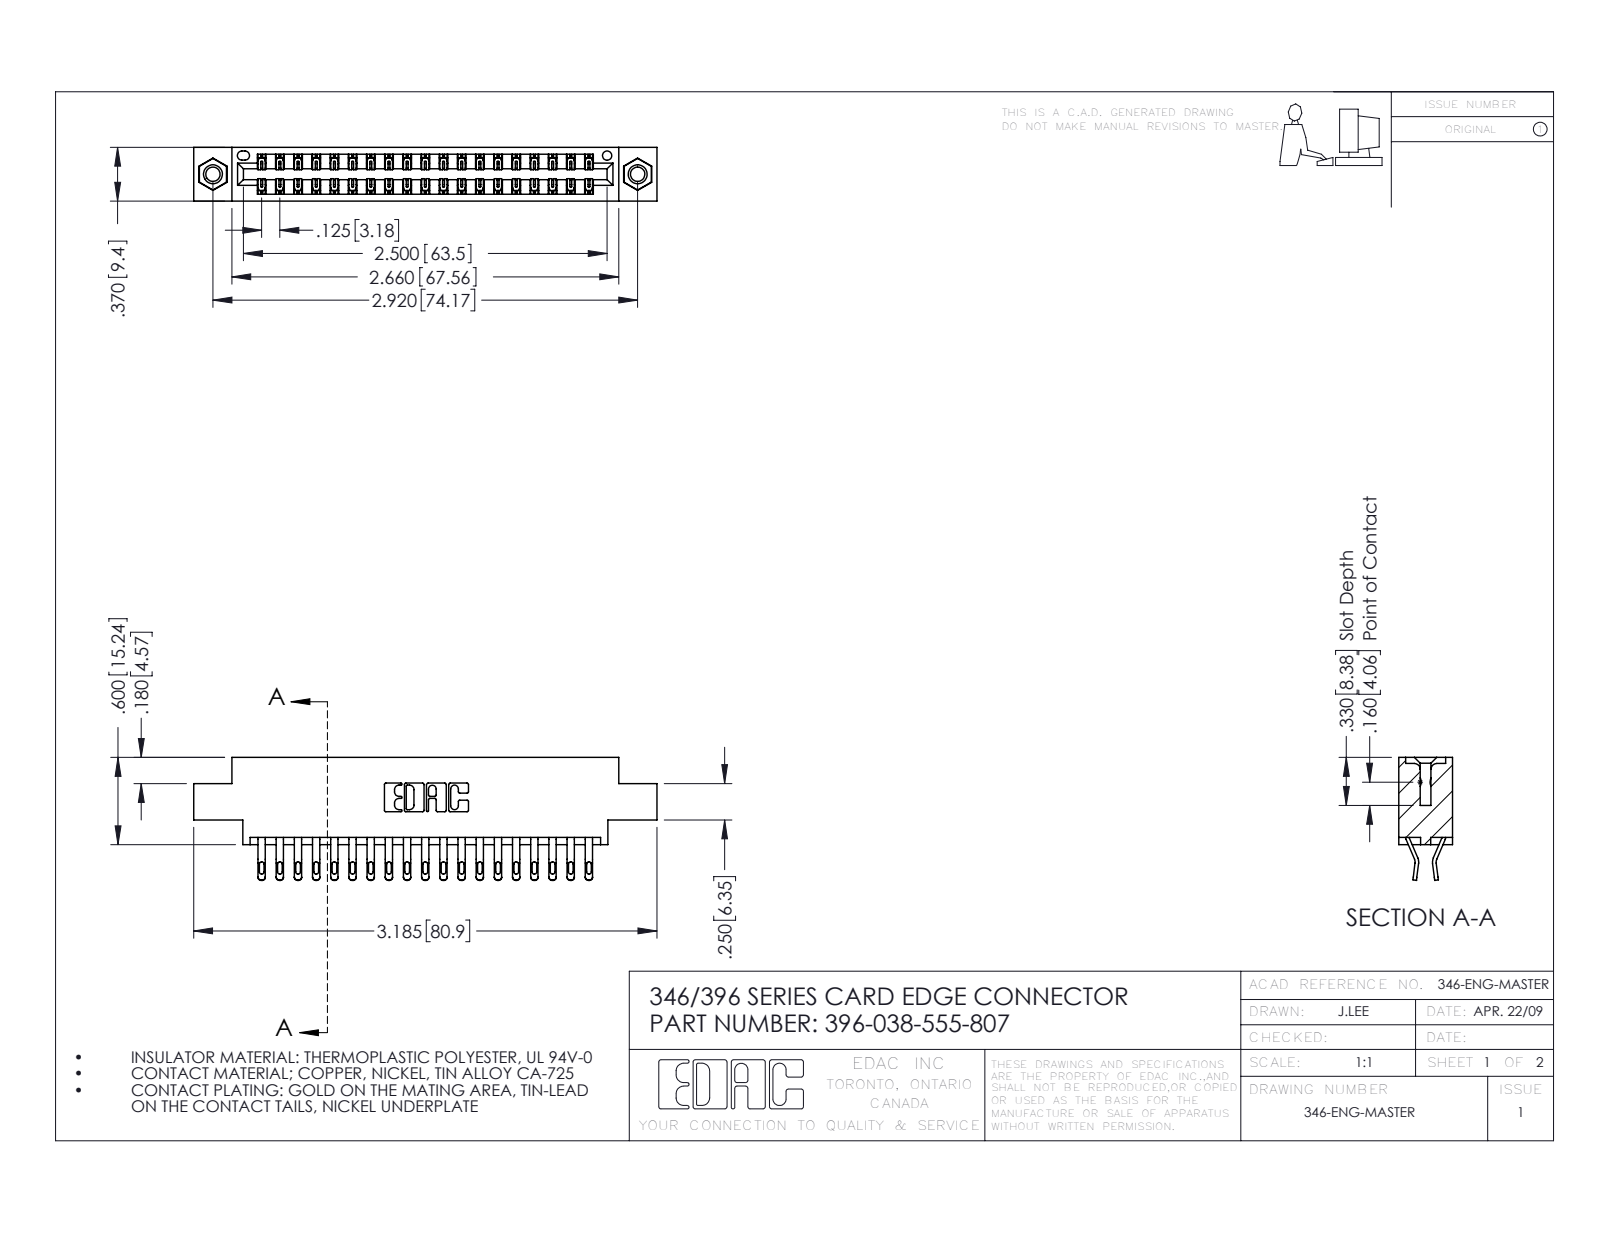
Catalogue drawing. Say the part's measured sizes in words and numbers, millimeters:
The part is named "396-038-555-807; 346 Part_0.170 Offset - 0.156 Dia-TI; 345-250-001_345-250-005-103; 345-292-001_555 Tail". Its 3-D file was written by "SolidWorks 2016 (CONFIG_CONTROL_DESIGN)". It is 41 solids with 2390 faces: 1366 planar, 1008 cylindrical and 16 other. Overall it measures 80.9 by 21.5 by 9.4 millimeters. Its volume is 7 650 cubic millimeters and its surface area 10 760 square millimeters. Round holes: 2 of diameter 2.5, 2 of diameter 3.2, 2 of diameter 4, 1 of diameter 1.6. Round bosses or shafts: 2 of diameter 3.9. Partial cylindrical surfaces (rounded edges, fillets, slot ends): 76 of radius 0.4, 76 of radius 0.5, 57 of radius 0.2, 22 of radius 0.3, 6 of radius 0.2, 6 of radius 0.8, 3 of radius 0.7, 2 of radius 0.3. The main face-to-face distances are 1.2, 8.2, 9.4, 6.4, 0.6, 1.8, 7.6, 7, 5.6, 3.8. The hole center spacings are 6.2, 68.9, 74.2.
